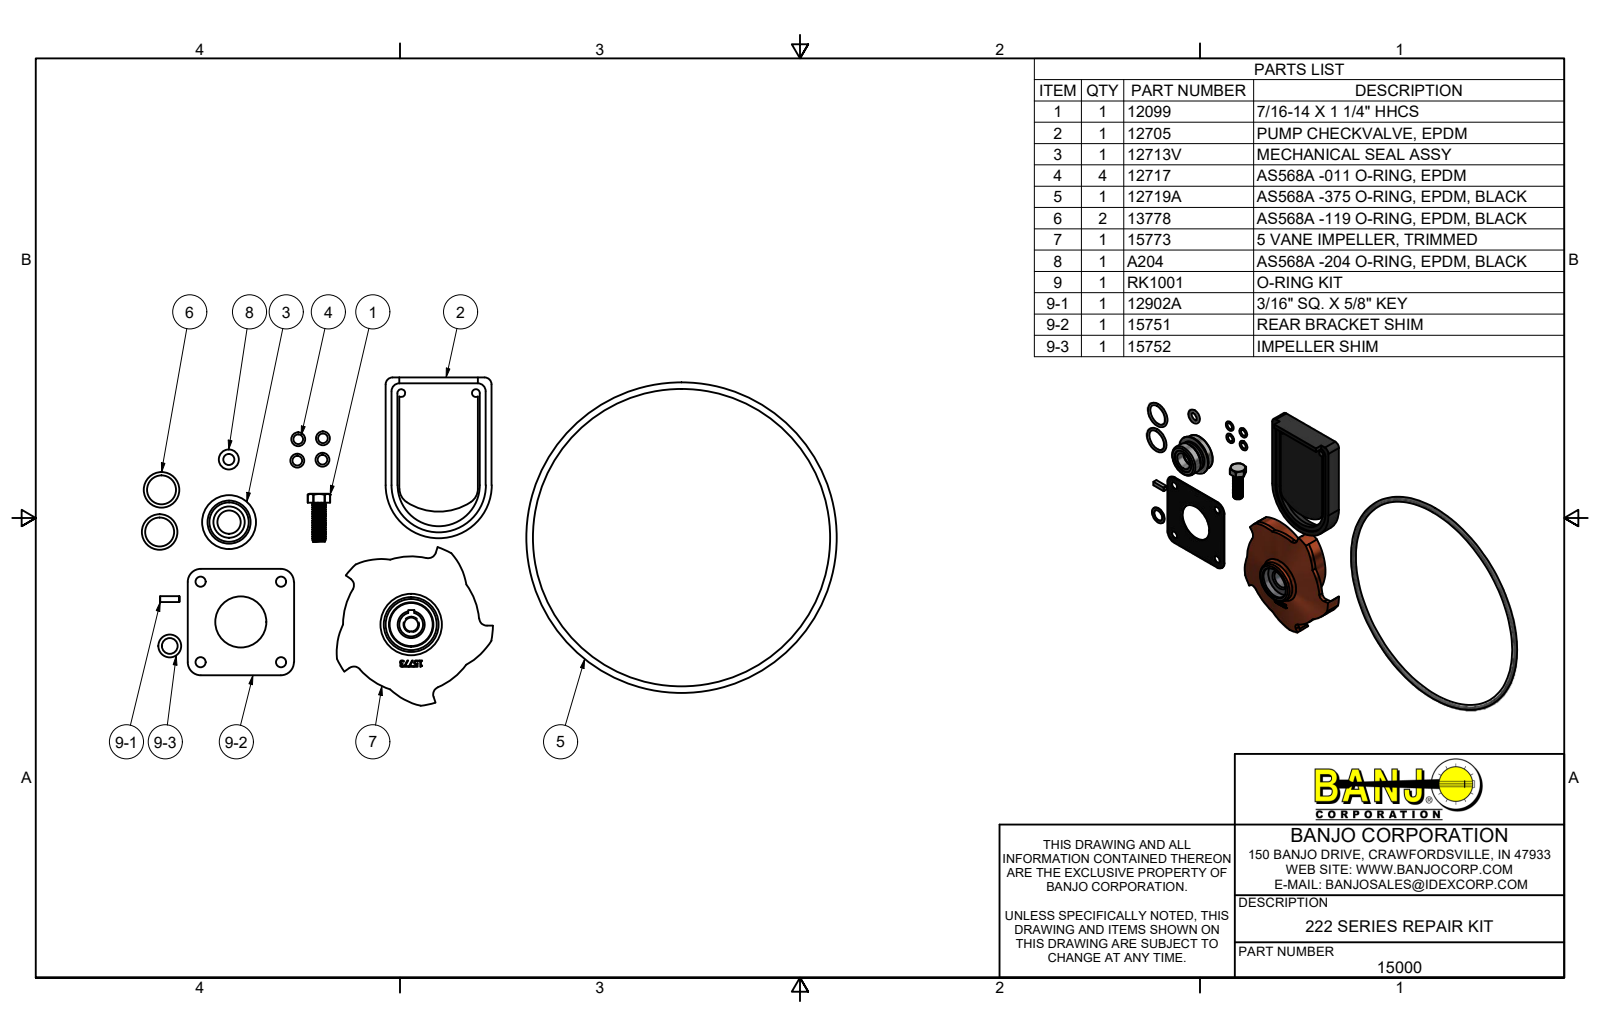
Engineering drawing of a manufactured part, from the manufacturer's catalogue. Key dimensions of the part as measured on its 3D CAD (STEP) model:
Part name (STEP PRODUCT): 15000; 12099; 12705; 12713V (+8 more)
STEP written by: Autodesk Inventor 2019 (AUTOMOTIVE_DESIGN)
Units: inches
Bodies: 16 solids, 367 faces (123 planar, 128 cylindrical, 116 other)
Overall size (bounding box): 22.153 × 10.455 × 1.41
Volume: 14.84 in³ · Surface area: 176.8 in²
Round holes (diameter × count): ⌀0.323 ×4, ⌀0.25 ×2, ⌀0.75 ×2, ⌀1 ×2, ⌀0.437 ×1, ⌀0.5 ×1, ⌀0.685 ×1, ⌀0.813 ×1, ⌀0.875 ×1, ⌀1.375 ×1, ⌀1.63 ×1
Round bosses / shafts (diameter × count): ⌀0.379 ×17, ⌀1.75 ×1, ⌀1.72 ×1, ⌀1.575 ×1, ⌀1.378 ×1, ⌀1.375 ×1, ⌀1.313 ×1, ⌀1.305 ×1
Partial cylindrical surfaces — rounded edges, fillets, slot ends (radius × count): R0.094 ×10, R0.25 ×7, R1.899 ×5, R2.086 ×5, R0.42 ×4, R0.03 ×2, R0.219 ×2, R0.313 ×2
Main face-to-face distances: 0.031, 0.02, 0.051, 0.188, 0.375, 0.563, 0.207, 0.239, 0.582, 0.613
Hole centre spacings: 2.563, 1.813, 3.625, 1.11, 1.812, 1.813, 2.104, 2.269
